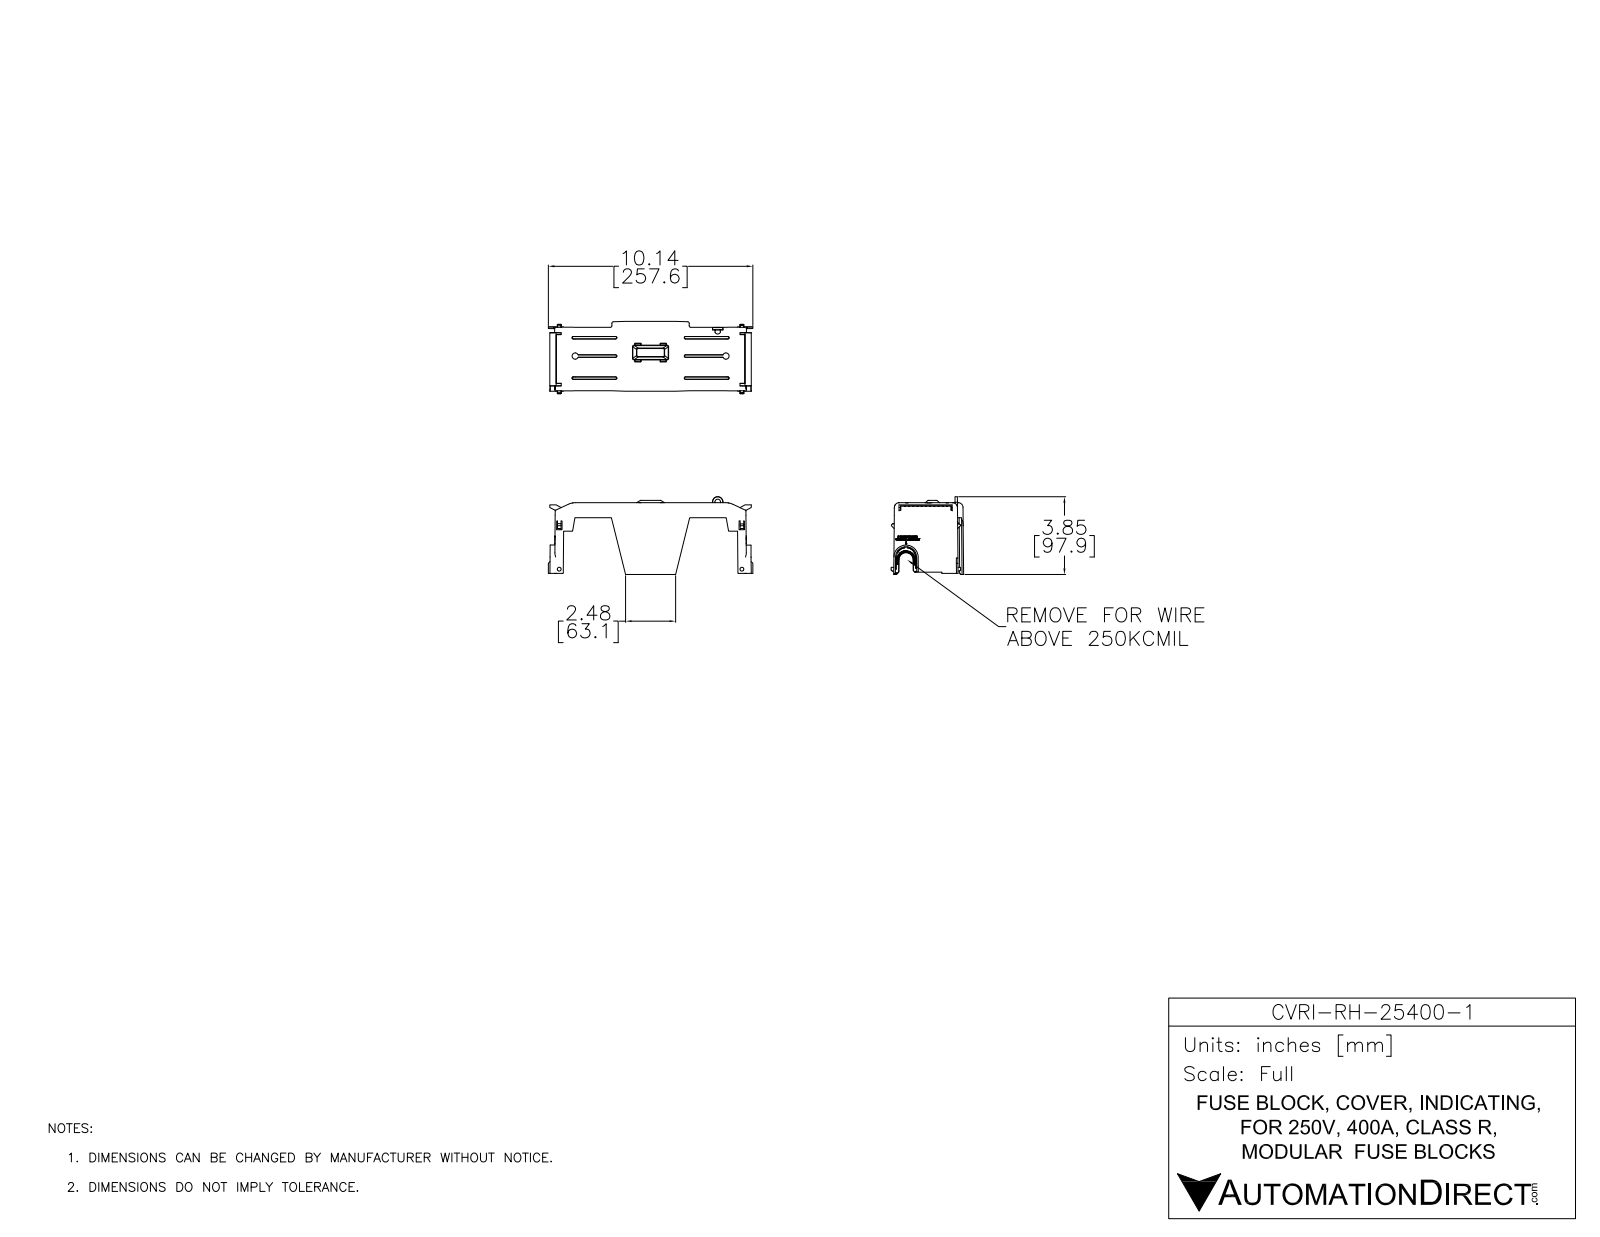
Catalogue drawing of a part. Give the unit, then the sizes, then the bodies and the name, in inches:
Units: inches
Overall size (bounding box): 10.143 × 3.853 × 3.593
Round holes (diameter × count): ⌀0.276 ×1
Partial cylindrical surfaces — rounded edges, fillets, slot ends (radius × count): R0.039 ×19, R0.118 ×8, R0.157 ×7, R0.236 ×7, R0.079 ×6, R0.01 ×2, R0.02 ×2, R0.232 ×2
Main face-to-face distances: 0.079, 0.276, 0.197, 0.354, 0.118, 0.669, 0.392, 1.338, 0.24, 1.098
Volume: 7.778 in³ · Surface area: 207.6 in²
Bodies: 1 solid, 2380 faces (1598 planar, 106 cylindrical, 676 other)
Part name (STEP PRODUCT): CVRI-RH-25400-1
STEP written by: SolidWorks 2017 (AUTOMOTIVE_DESIGN)
